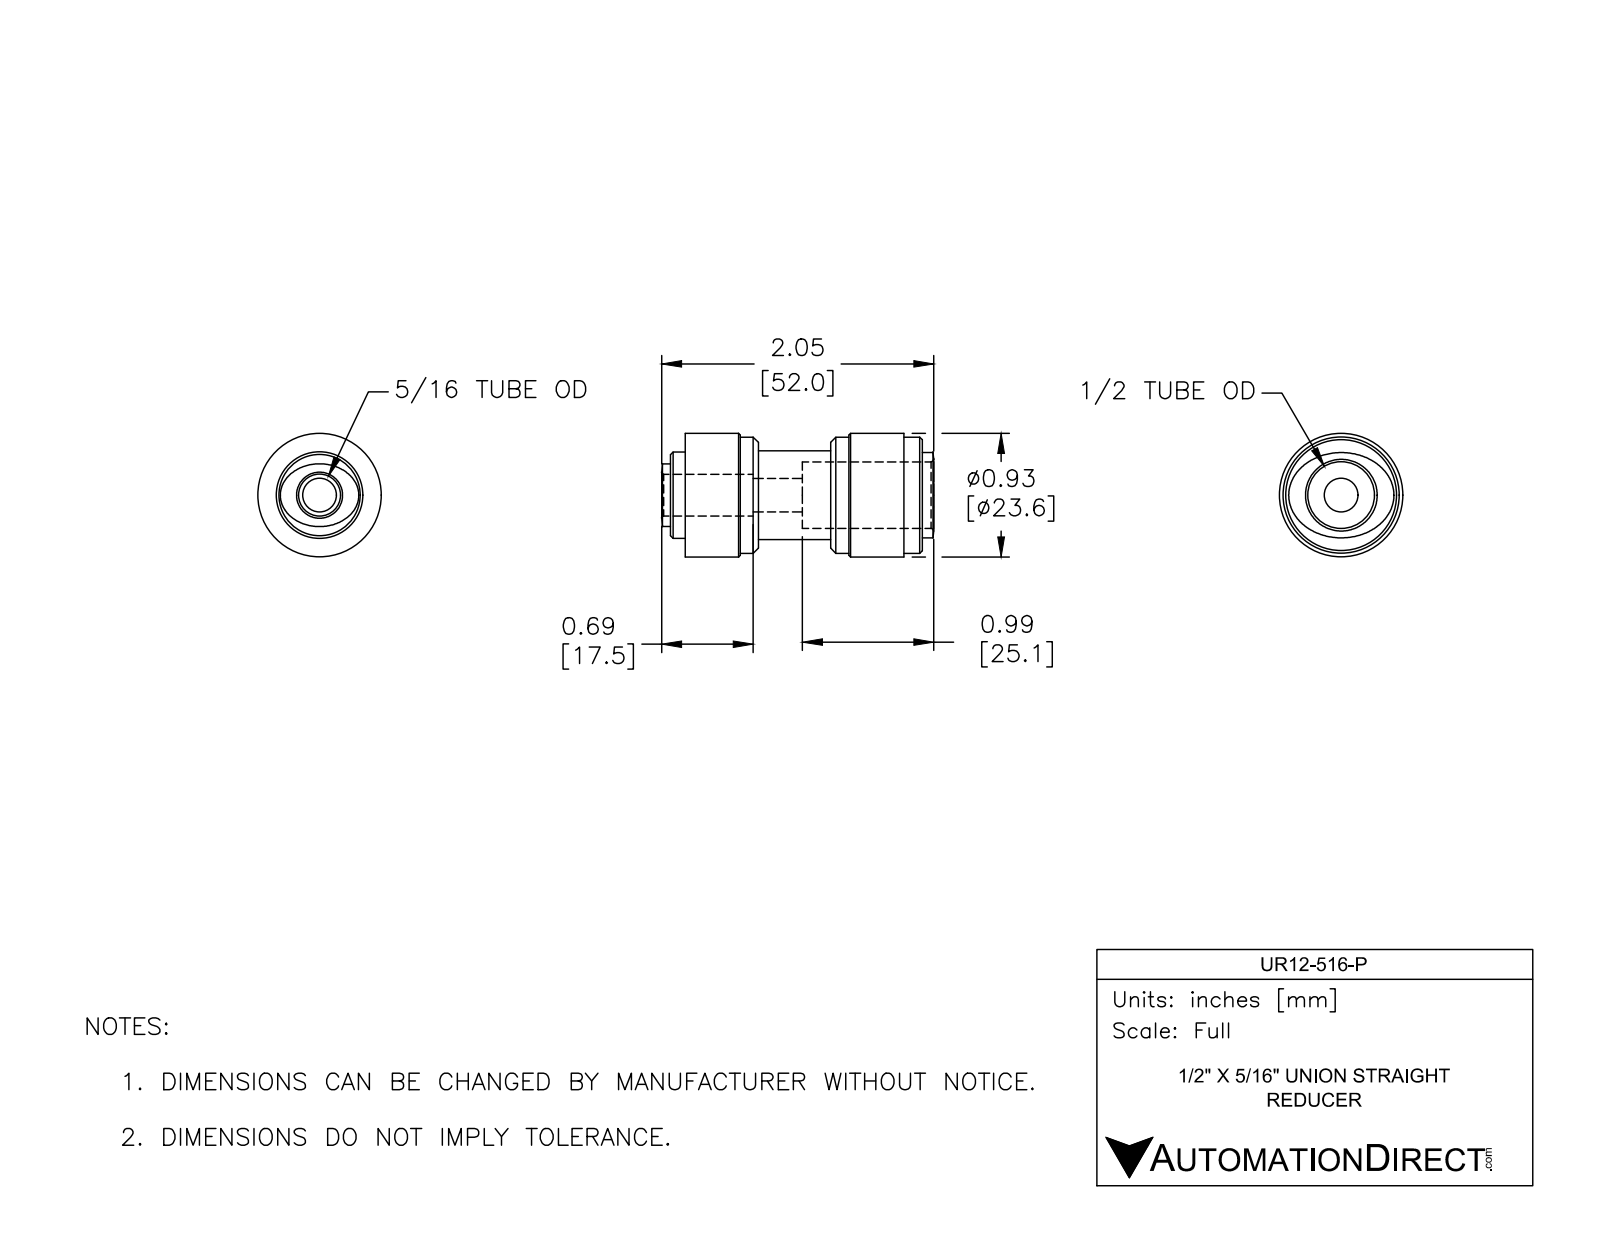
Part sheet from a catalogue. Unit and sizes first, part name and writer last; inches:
Units: inches
Overall size (bounding box): 2.047 × 0.929 × 0.929
Round holes (diameter × count): ⌀0.252 ×1, ⌀0.315 ×1, ⌀0.5 ×1
Round bosses / shafts (diameter × count): ⌀0.929 ×1, ⌀0.874 ×1, ⌀0.669 ×1, ⌀0.65 ×1
Main face-to-face distances: 0.551, 1.232, 1.094, 0.138, 1.783, 0.902, 0.882, 0.331, 0.689, 0.213
Volume: 0.813 in³ · Surface area: 9.388 in²
Bodies: 1 solid, 54 faces (10 planar, 20 cylindrical, 24 other)
Part name (STEP PRODUCT): UR12-516-P
STEP written by: SolidWorks 2017 (AUTOMOTIVE_DESIGN)
